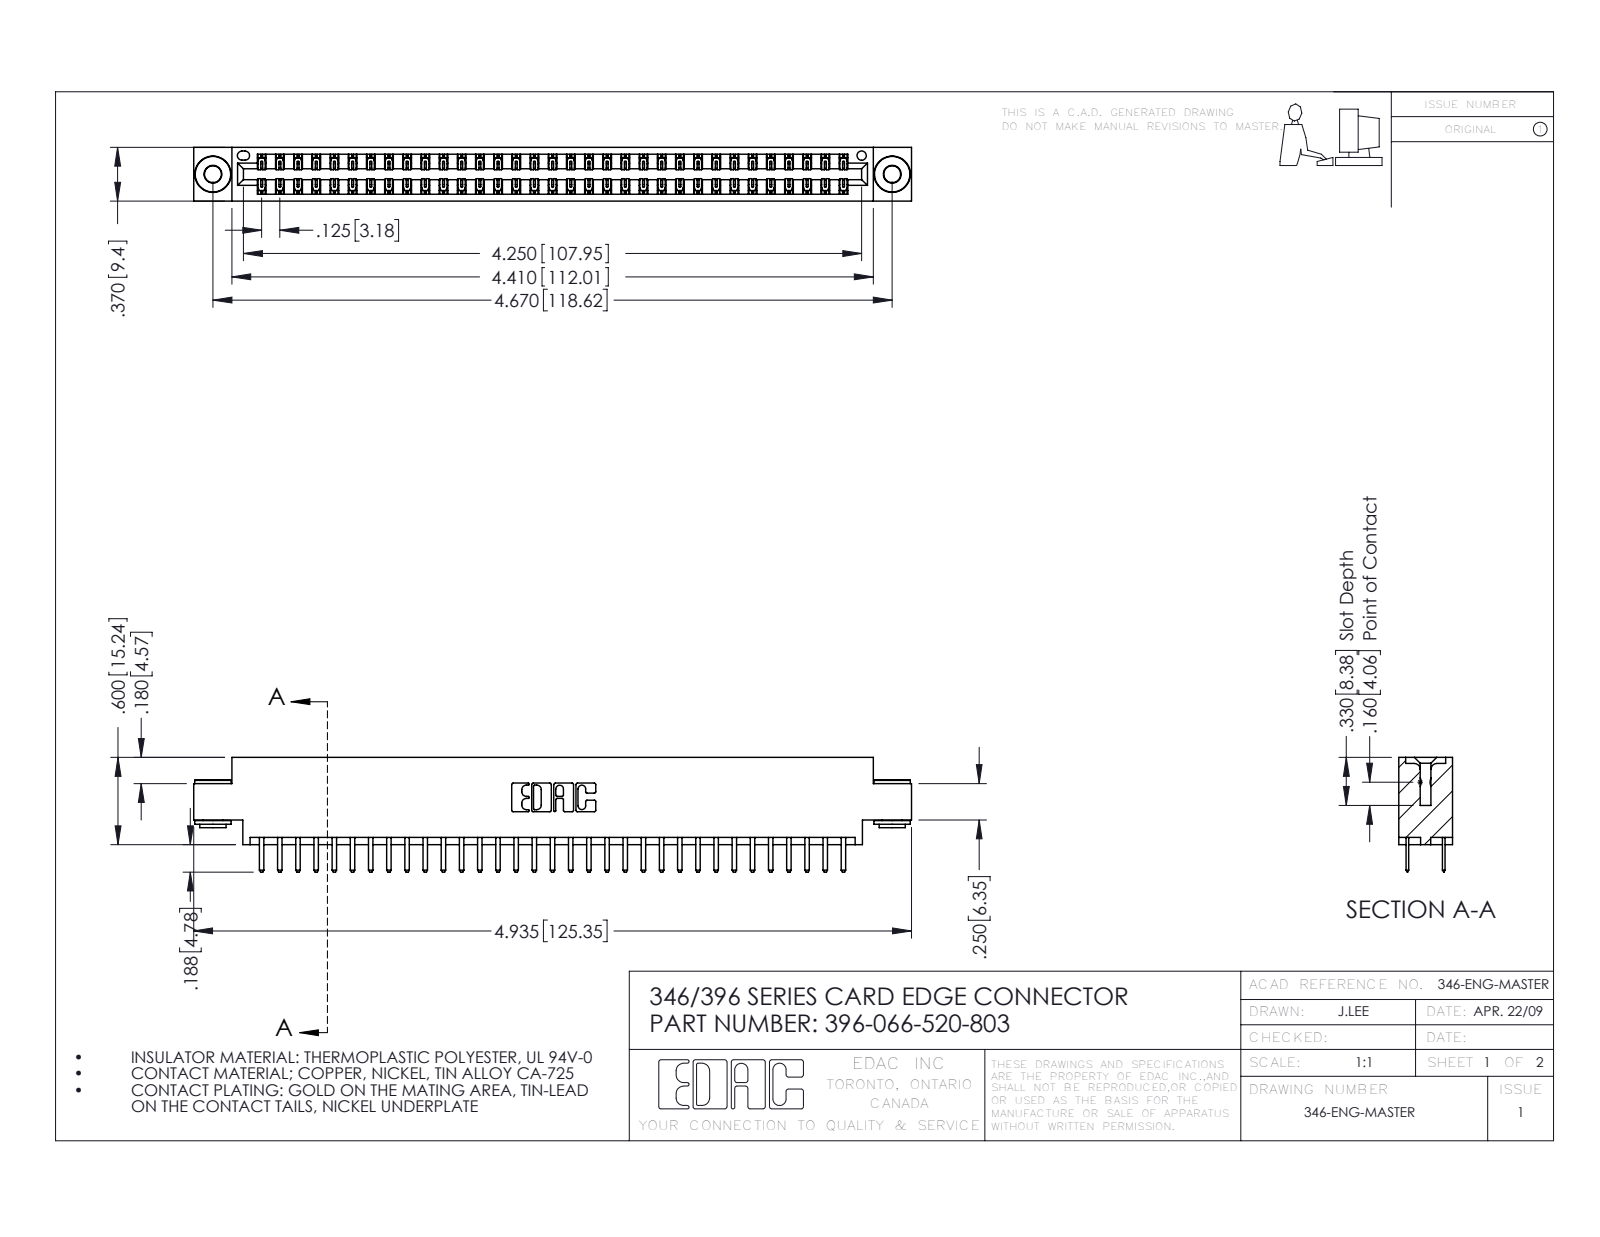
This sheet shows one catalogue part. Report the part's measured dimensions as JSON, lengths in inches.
{"part_name": "345-250-002_345-250-002-102; 346 Part_0.170 Offset - 0.156 Dia-TH; 396-066-520-803; 345-292-001_345-293-120", "step_written_by": "SolidWorks 2016 (CONFIG_CONTROL_DESIGN)", "units": "inches", "bodies": {"solids": 69, "faces": 3860, "planar": 2532, "cylindrical": 1320, "other": 8}, "overall_size": [4.935, 0.788, 0.37], "volume_in3": 0.732, "surface_area_in2": 25.83, "round_holes": [[0.116, 2], [0.156, 2], [0.064, 1]], "round_bosses_or_shafts": [[0.25, 2], [0.18, 2], [0.136, 2]], "partial_cylinders_radius": [[0.006, 99], [0.01, 70], [0.01, 22], [0.007, 6], [0.031, 6], [0.026, 3], [0.014, 2], [0.022, 2]], "face_to_face_distances": [0.048, 0.322, 0.37, 0.25, 0.025, 0.275, 0.072, 0.298, 0.148, 0.222], "hole_center_spacings": [0.246, 4.462, 4.67]}
